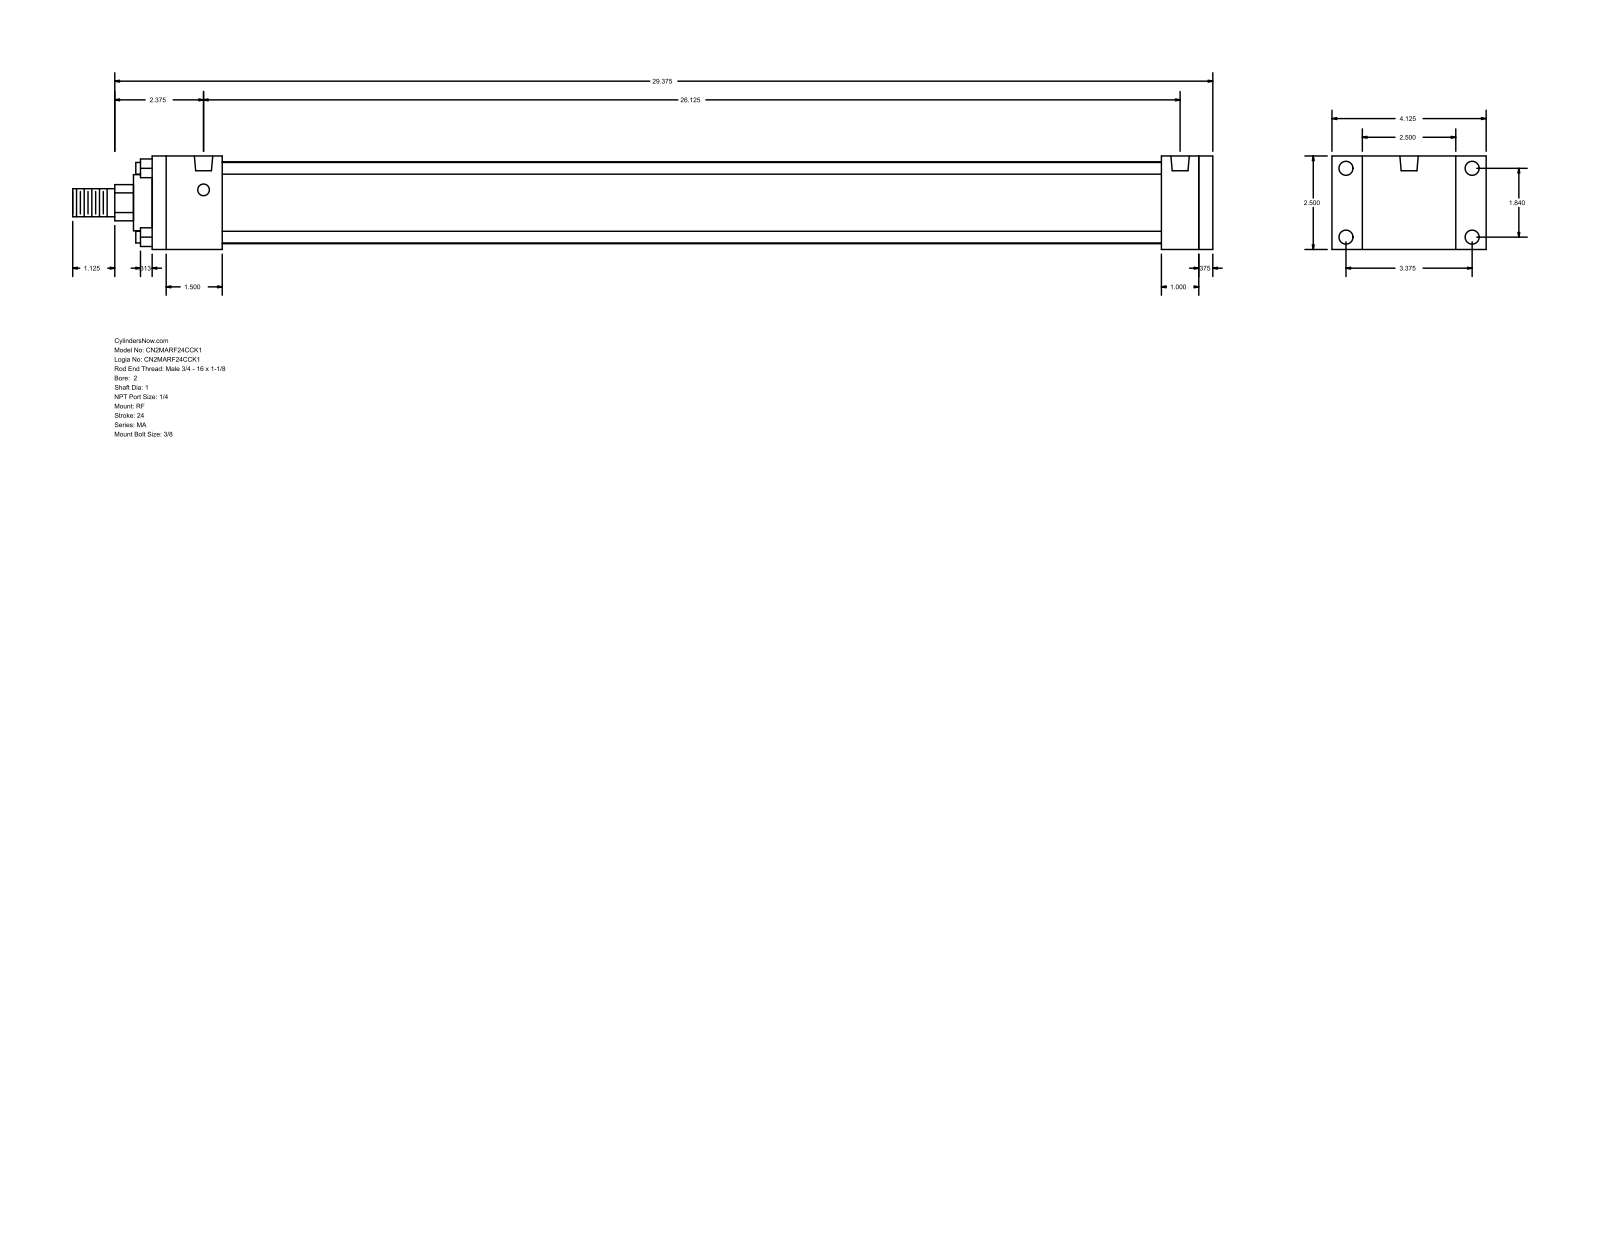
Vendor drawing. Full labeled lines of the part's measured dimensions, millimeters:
Part name (STEP PRODUCT): MA_RF__0200_1
STEP written by: GSSL Pune (CONFIG_CONTROL_DESIGN)
Units: millimetres
Bodies: 0 solids, 92 faces (64 planar, 28 cylindrical, 0 other)
Overall size (bounding box): 774.7 × 104.78 × 63.5
Round holes (diameter × count): ⌀7.94 ×4, ⌀9.53 ×4, ⌀12.49 ×2
Round bosses / shafts (diameter × count): ⌀7.94 ×4, ⌀55.63 ×1, ⌀38.1 ×1, ⌀25.4 ×1, ⌀19.05 ×1
Partial cylindrical surfaces — rounded edges, fillets, slot ends (radius × count): R12.29 ×1
Main face-to-face distances: 63.5, 711.2, 9.52, 720.72, 25.4, 20.64, 12.7, 47.63, 663.57, 673.09
Hole centre spacings: 46.74, 85.72, 97.63, 663.57
